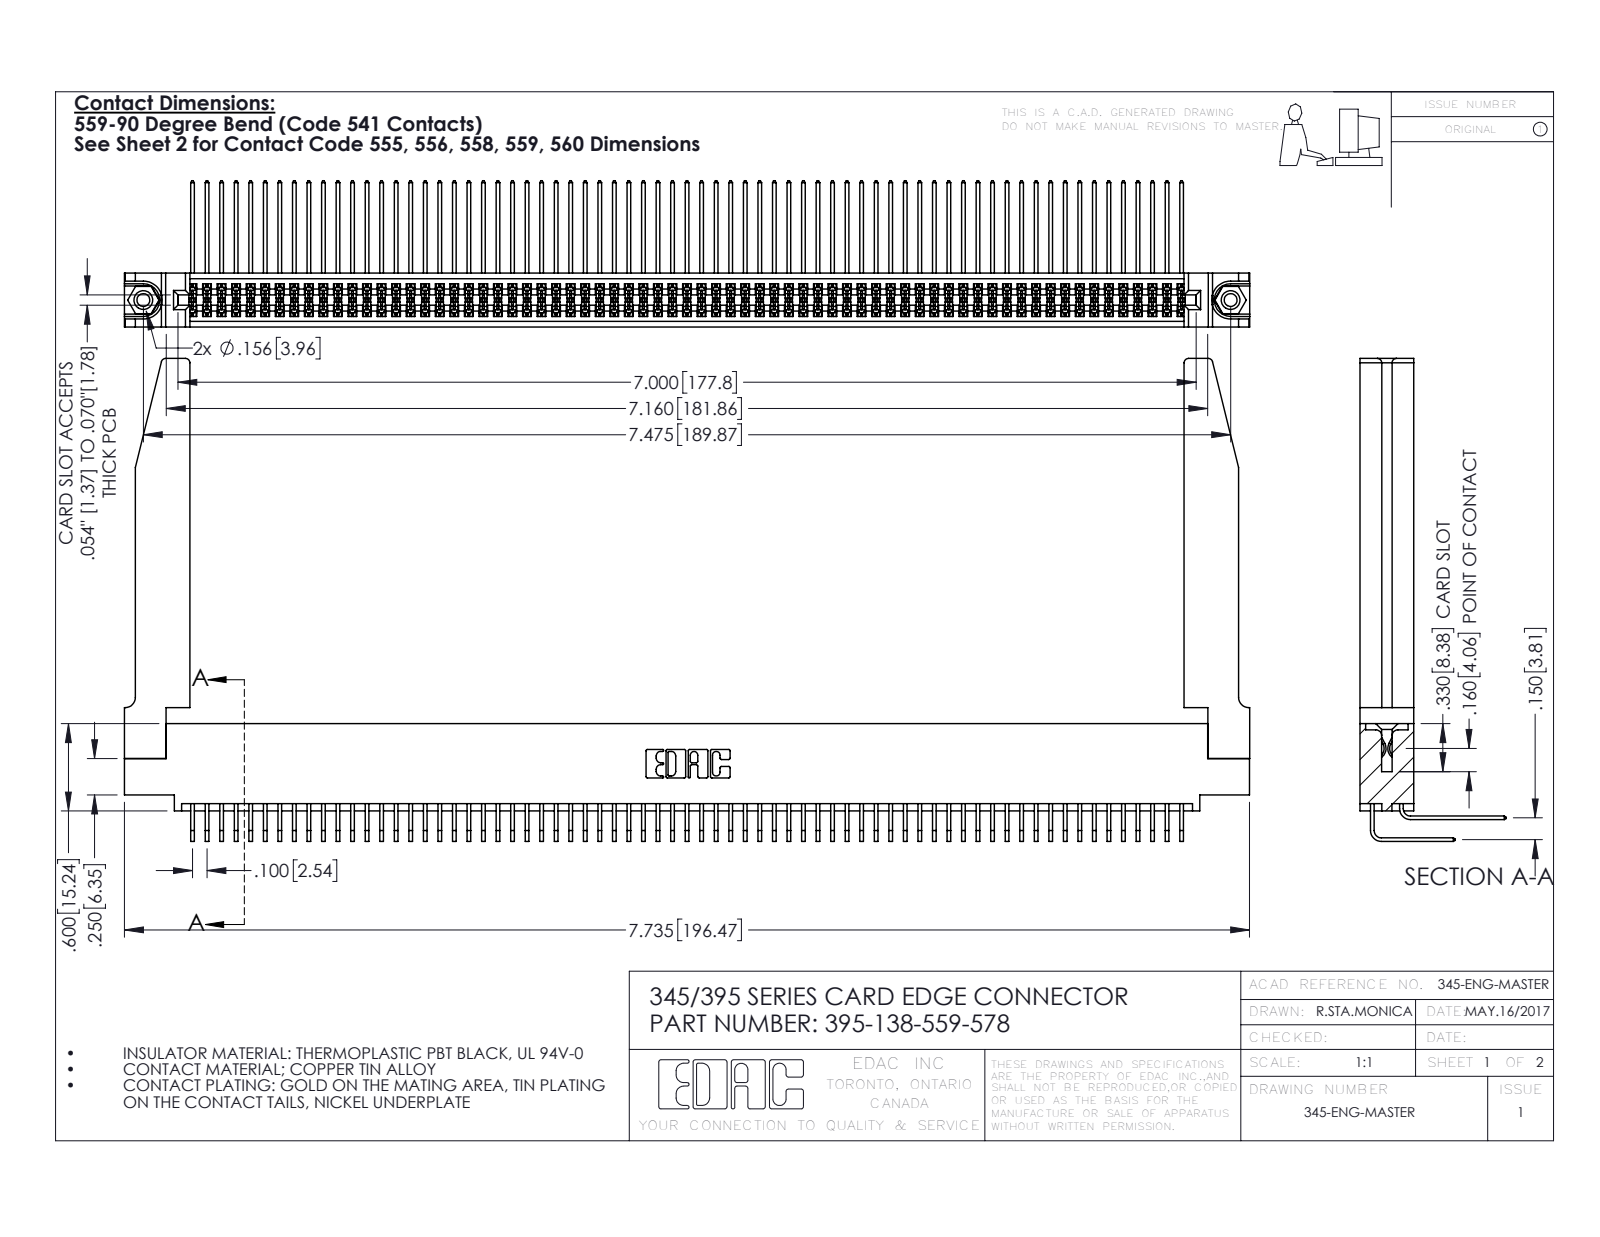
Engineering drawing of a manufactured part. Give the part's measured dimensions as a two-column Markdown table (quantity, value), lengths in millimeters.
| quantity | value |
| --- | --- |
| part name | 395-138-559-578; 345-220-078_345-220-078; 345-292-001_558 559 Tail - 1; 345 Part_0.110 Offset - 0.156 Dia-TH (+2 more) |
| STEP written by | SolidWorks 2016 (CONFIG_CONTROL_DESIGN) |
| units | millimeters |
| bodies | 143 solids, 7540 faces (5056 planar, 2432 cylindrical, 52 other) |
| overall size | 196.5 × 84.3 × 25.5 |
| volume | 27 830 mm³ |
| surface area | 40 850 mm² |
| round holes (diameter × count) | 2.3 × 2, 3.2 × 2, 4 × 2, 1.6 × 1 |
| round bosses / shafts (diameter × count) | 3.9 × 2 |
| partial cylindrical surfaces (radius × count) | 0.2 × 275, 0.3 × 22, 0.8 × 8, 0.2 × 6, 0.8 × 6, 0.7 × 3, 0.4 × 2, 0.5 × 2 |
| main face-to-face distances | 1.8, 7.6, 9.4, 2.5, 6.9, 0.6, 5.1, 5.7, 4.4, 3.8 |
| hole center spacings | 6.9, 183.9, 189.9 |
